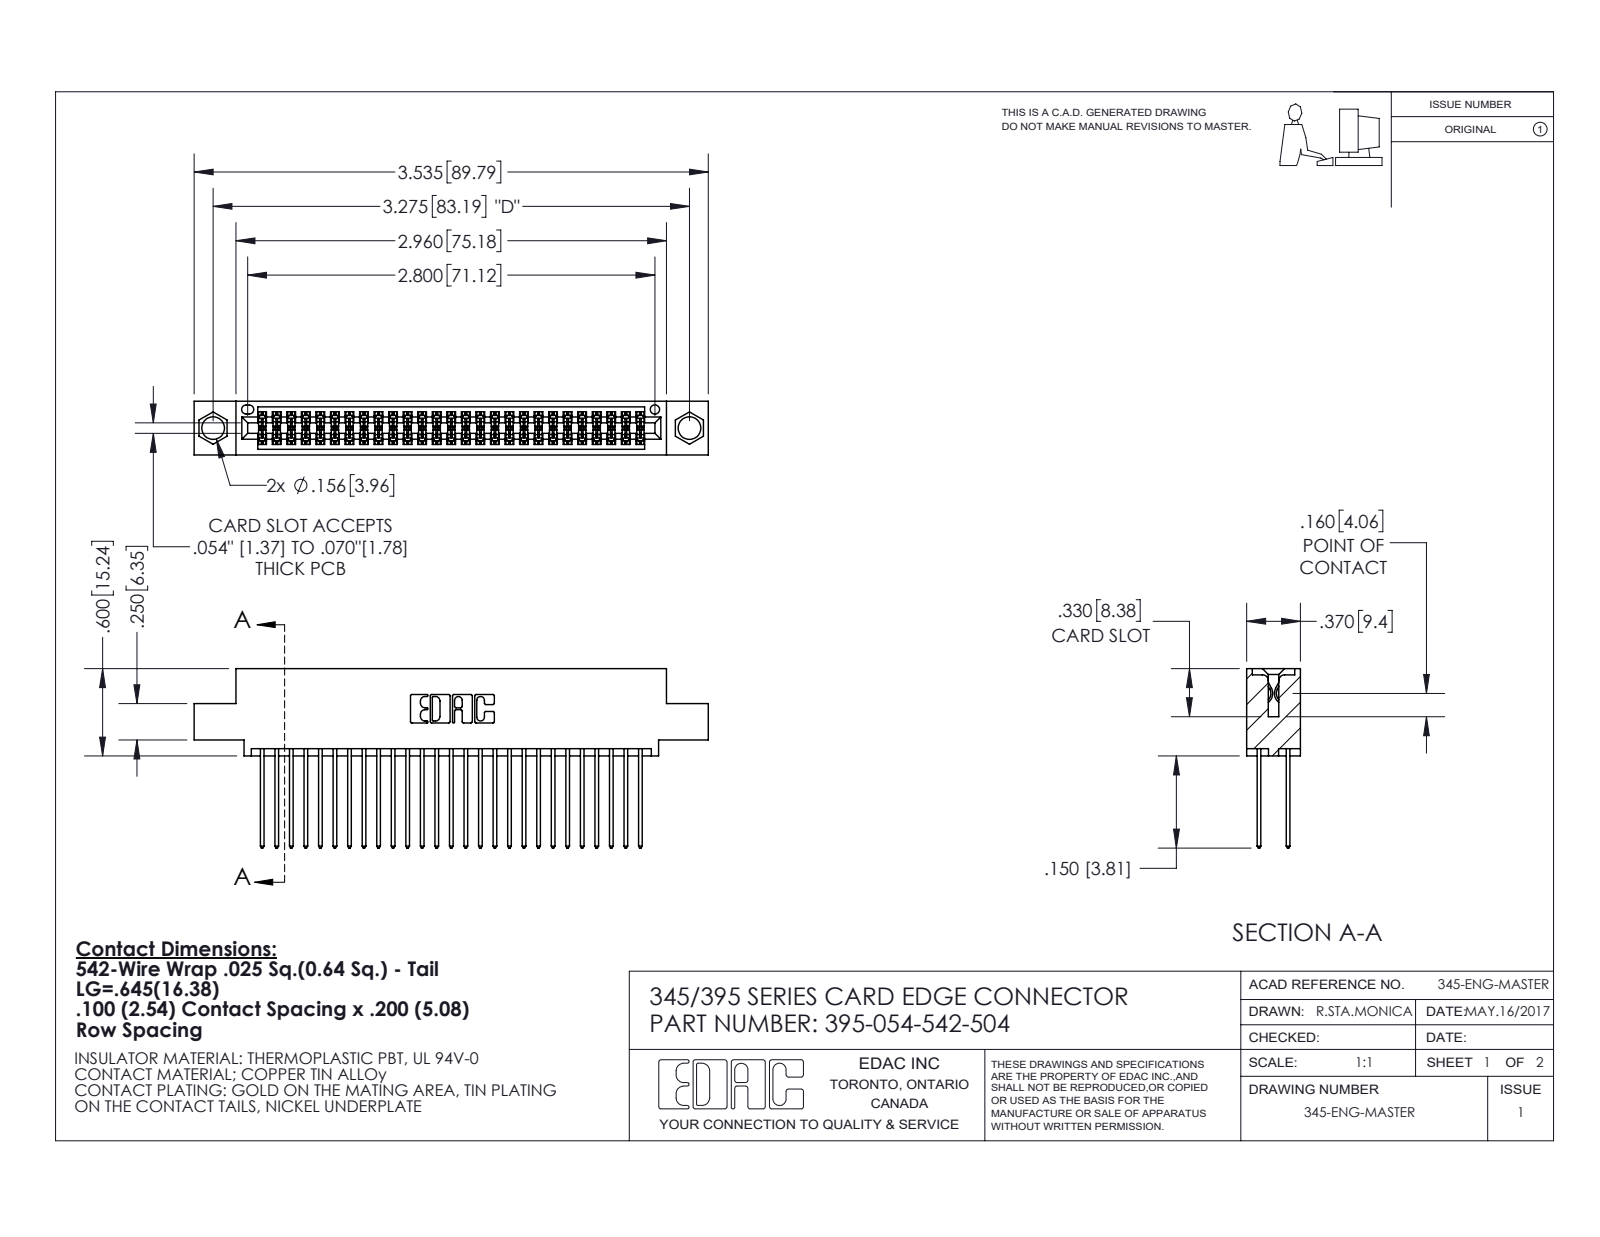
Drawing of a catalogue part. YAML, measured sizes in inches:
part_name: "345 Part_0.110 Offset - 0.156 Dia-TI; 345-292-001_345-293-142; 395-054-542-504"
step_written_by: "SolidWorks 2020 (CONFIG_CONTROL_DESIGN)"
units: inches
bodies: {solids: 55, faces: 2844, planar: 1880, cylindrical: 964, other: 0}
overall_size: [3.535, 1.232, 0.37]
volume: 0.528
surface_area: 21.12
round_holes:
  - {diameter: 0.156, count: 2}
  - {diameter: 0.064, count: 1}
partial_cylinders:
  - {radius: 0.006, count: 108}
  - {radius: 0.01, count: 54}
  - {radius: 0.01, count: 22}
  - {radius: 0.007, count: 6}
  - {radius: 0.031, count: 6}
  - {radius: 0.026, count: 3}
  - {radius: 0.014, count: 2}
  - {radius: 0.019, count: 2}
face_to_face_distances: [0.072, 0.298, 0.2, 0.098, 0.272, 0.025, 0.37, 0.225, 0.175, 0.149]
hole_center_spacings: [0.27, 3.04, 3.275]
